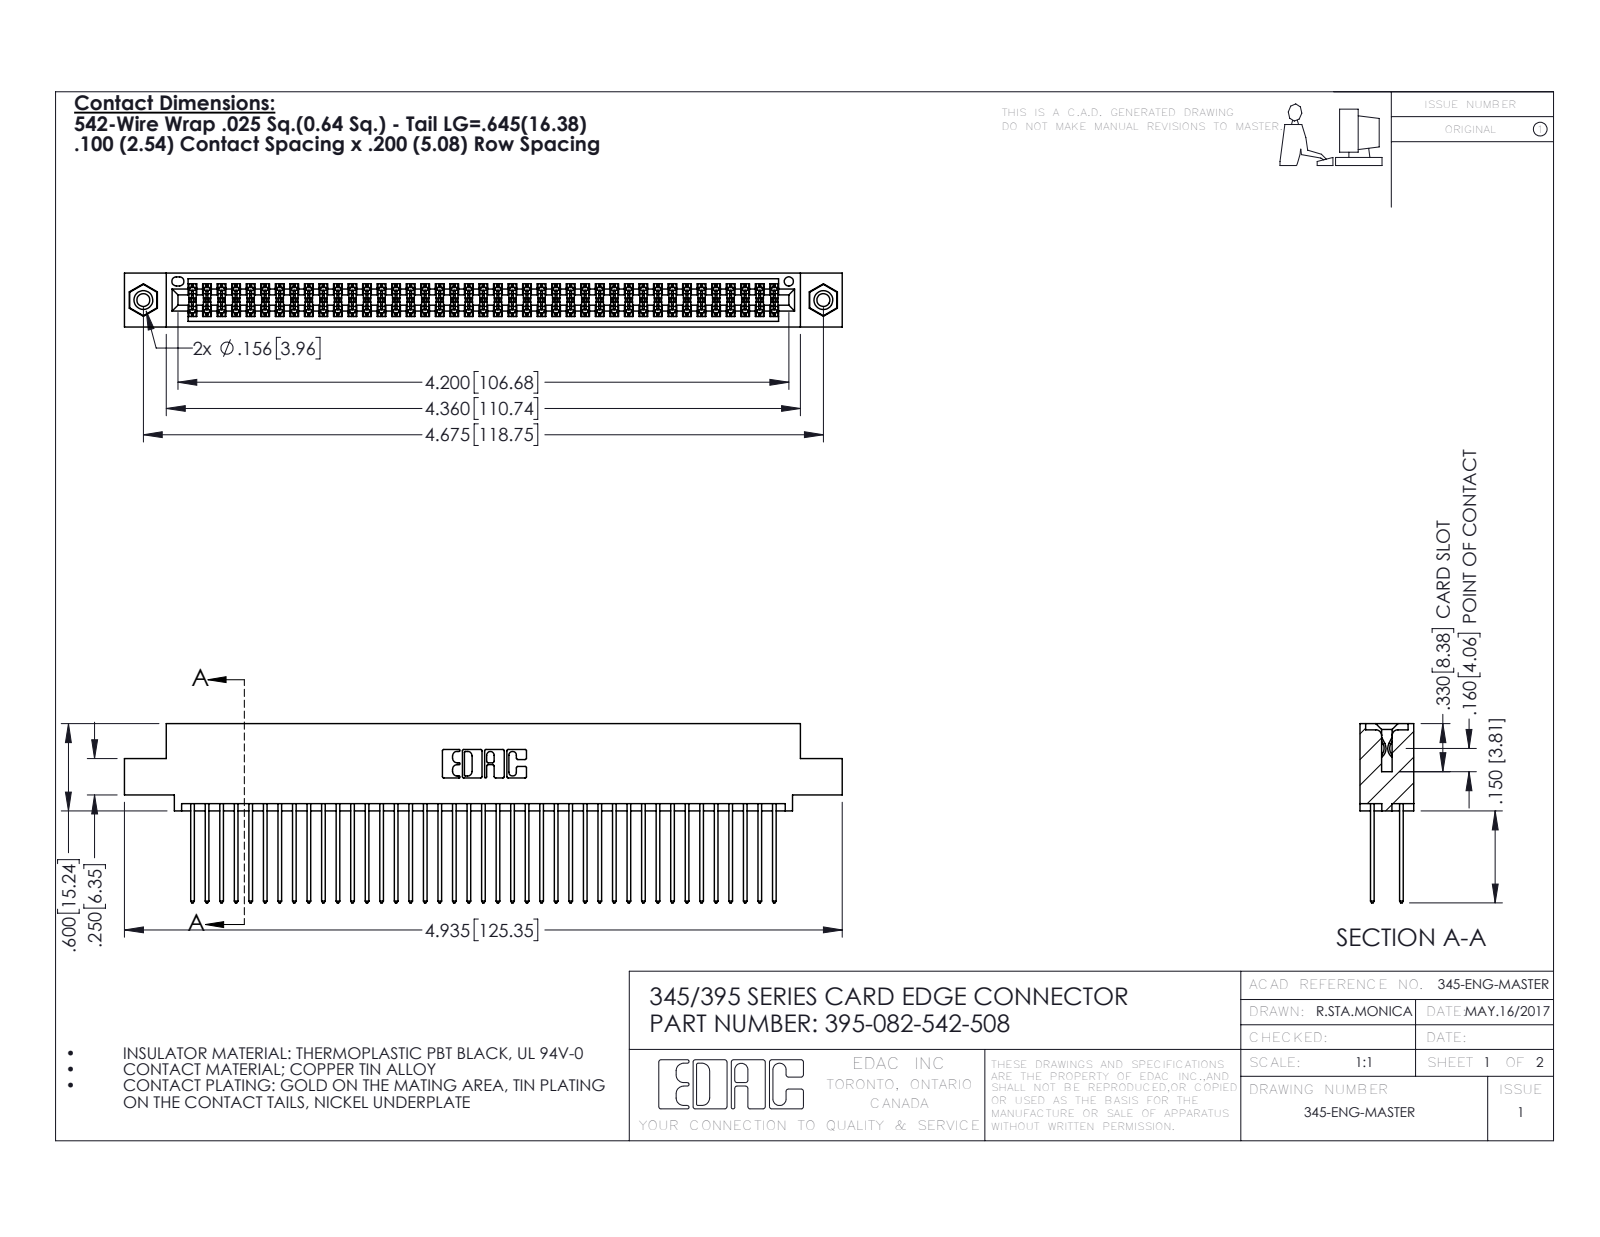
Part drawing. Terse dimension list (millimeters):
name: 345 Part_0.110 Offset - 0.156 Dia-TI; 395-082-542-508; 345-292-001_345-293-142; 345-250-001_345-250-003-102
written by: SolidWorks 2016 (CONFIG_CONTROL_DESIGN)
unit: mm
bodies: 85 solids, 4290 faces (2822 planar, 1452 cylindrical, 16 other)
size: 125.3 × 31.3 × 9.4
volume: 12 500 mm³; area: 20 300 mm²
holes: 2× ⌀2.3, 2× ⌀3.2, 2× ⌀4, 1× ⌀1.6
bosses: 2× ⌀3.9
rounds: 123× R0.2, 82× R0.3, 22× R0.3, 6× R0.2, 6× R0.8, 3× R0.7, 2× R0.4, 2× R0.5
face distances: 1.8, 7.6, 5.1, 2.5, 6.9, 0.6, 5.7, 9.4, 4.4, 3.8
hole spacings: 6.9, 112.8, 118.7
